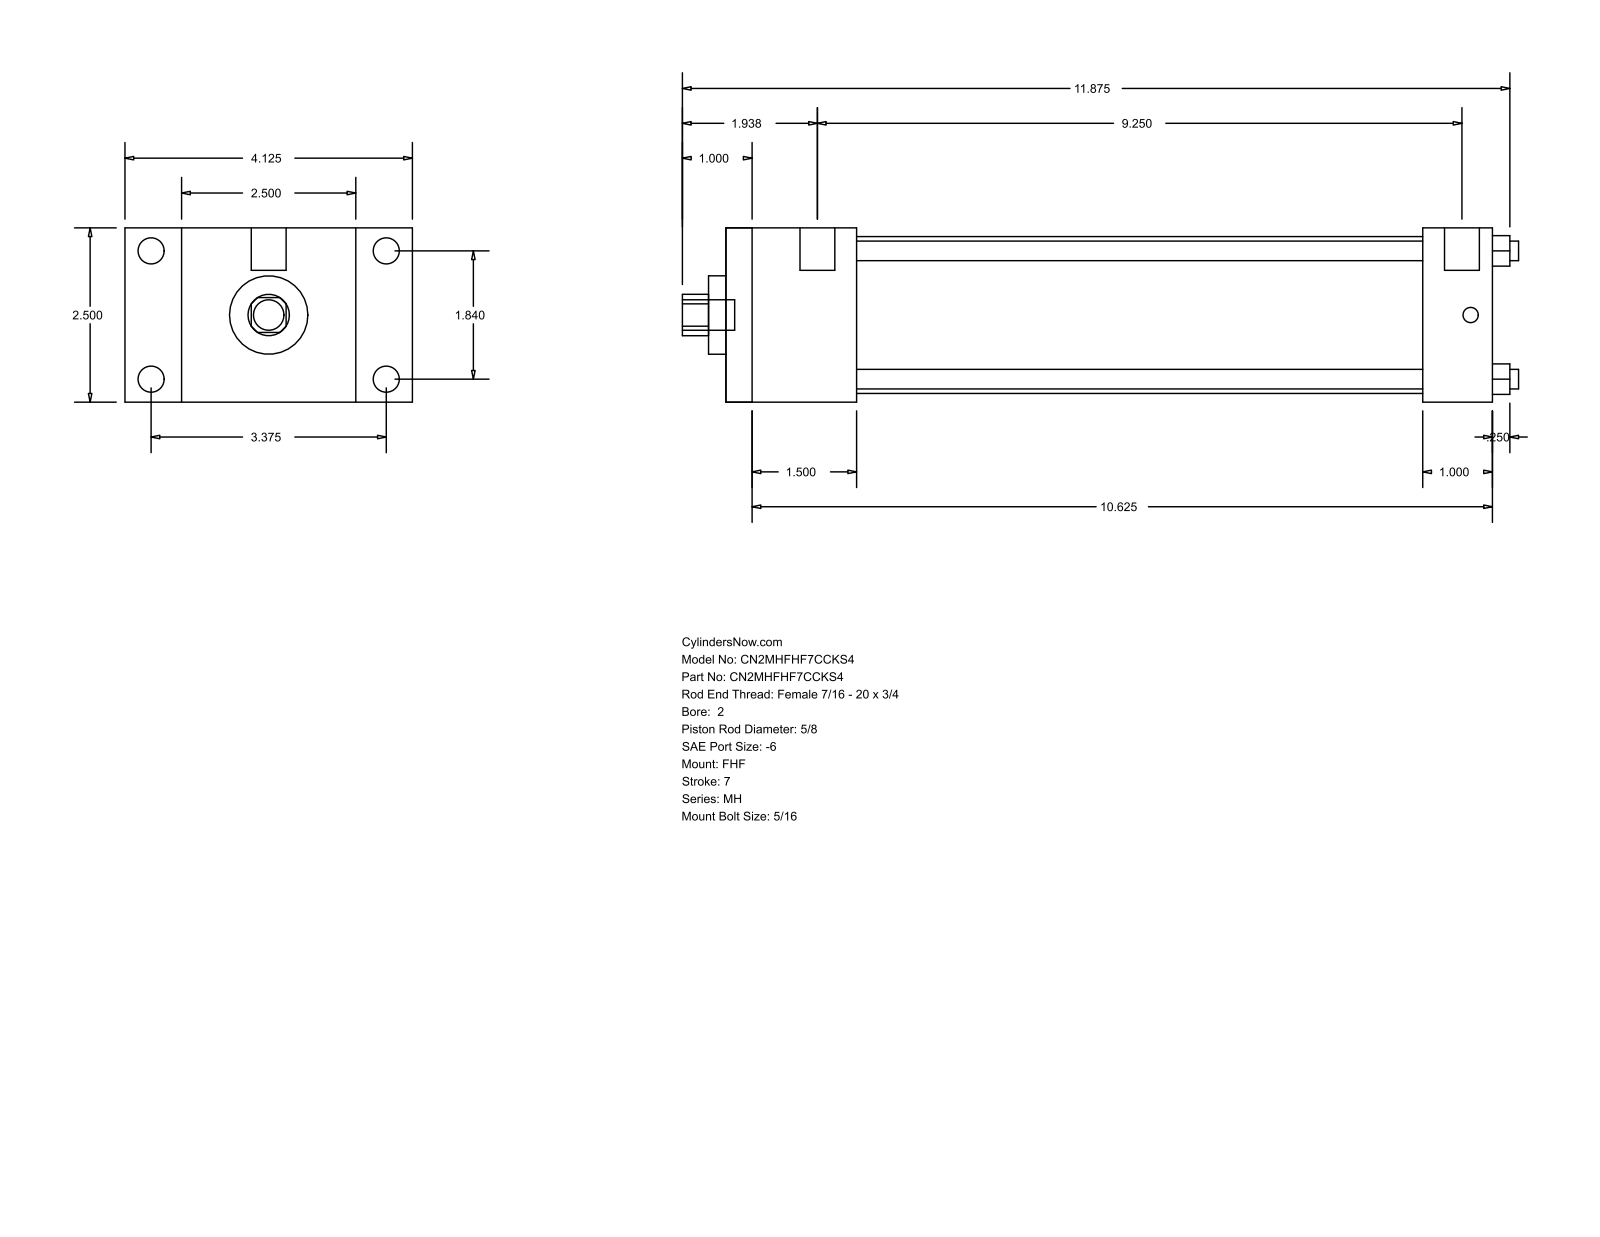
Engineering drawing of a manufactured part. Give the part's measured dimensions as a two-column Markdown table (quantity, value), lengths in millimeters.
| quantity | value |
| --- | --- |
| part name | MH_FHF__0200_0.625 |
| STEP written by | GSSL Pune (CONFIG_CONTROL_DESIGN) |
| units | millimeters |
| bodies | 0 solids, 88 faces (60 planar, 28 cylindrical, 0 other) |
| overall size | 304.8 × 104.78 × 63.5 |
| round holes (diameter × count) | 7.14 × 4, 15.88 × 1, 28.57 × 1, 57.15 × 1 |
| round bosses / shafts (diameter × count) | 9.53 × 4, 5.56 × 4, 12.7 × 2, 11.11 × 1 |
| partial cylindrical surfaces (radius × count) | 7.54 × 1 |
| main face-to-face distances | 63.5, 47.62, 279.39, 231.77, 20.64, 84.14, 104.78, 254, 206.38, 25.39 |
| hole center spacings | 33.05, 46.74, 66.1 |
